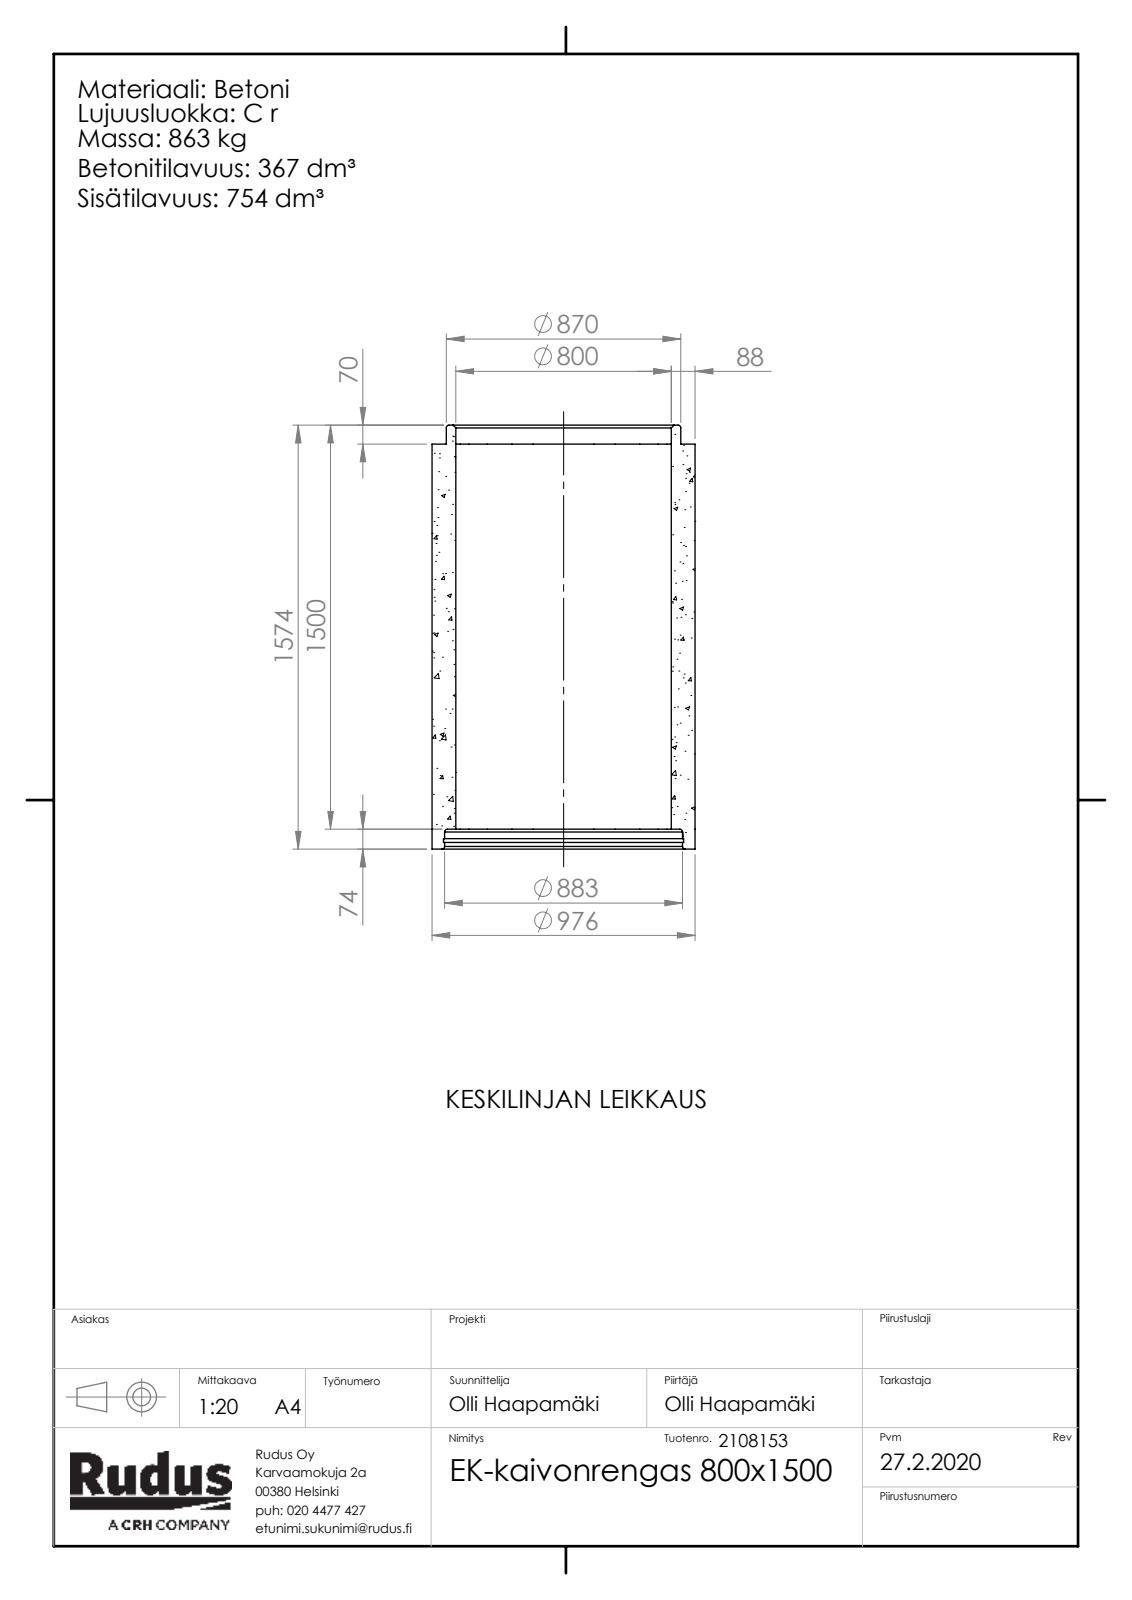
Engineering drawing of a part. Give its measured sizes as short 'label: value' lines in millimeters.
name: Rudus 2108153 EK-kaivonrengas 800x1500; EK-osa-kaivorunko_EK-kaivonrengas
written by: SolidWorks 2019 (CONFIG_CONTROL_DESIGN)
unit: mm
bodies: 1 solid, 107 faces (6 planar, 12 cylindrical, 89 other)
size: 1574 × 976 × 976
volume: 367 200 000 mm³; area: 9 246 000 mm²
holes: 1× ⌀800, 1× ⌀883, 1× ⌀891
bosses: 1× ⌀976, 1× ⌀870
face distances: 1504, 74, 1430, 1574, 1500, 70, 39, 35, 1465, 1535
